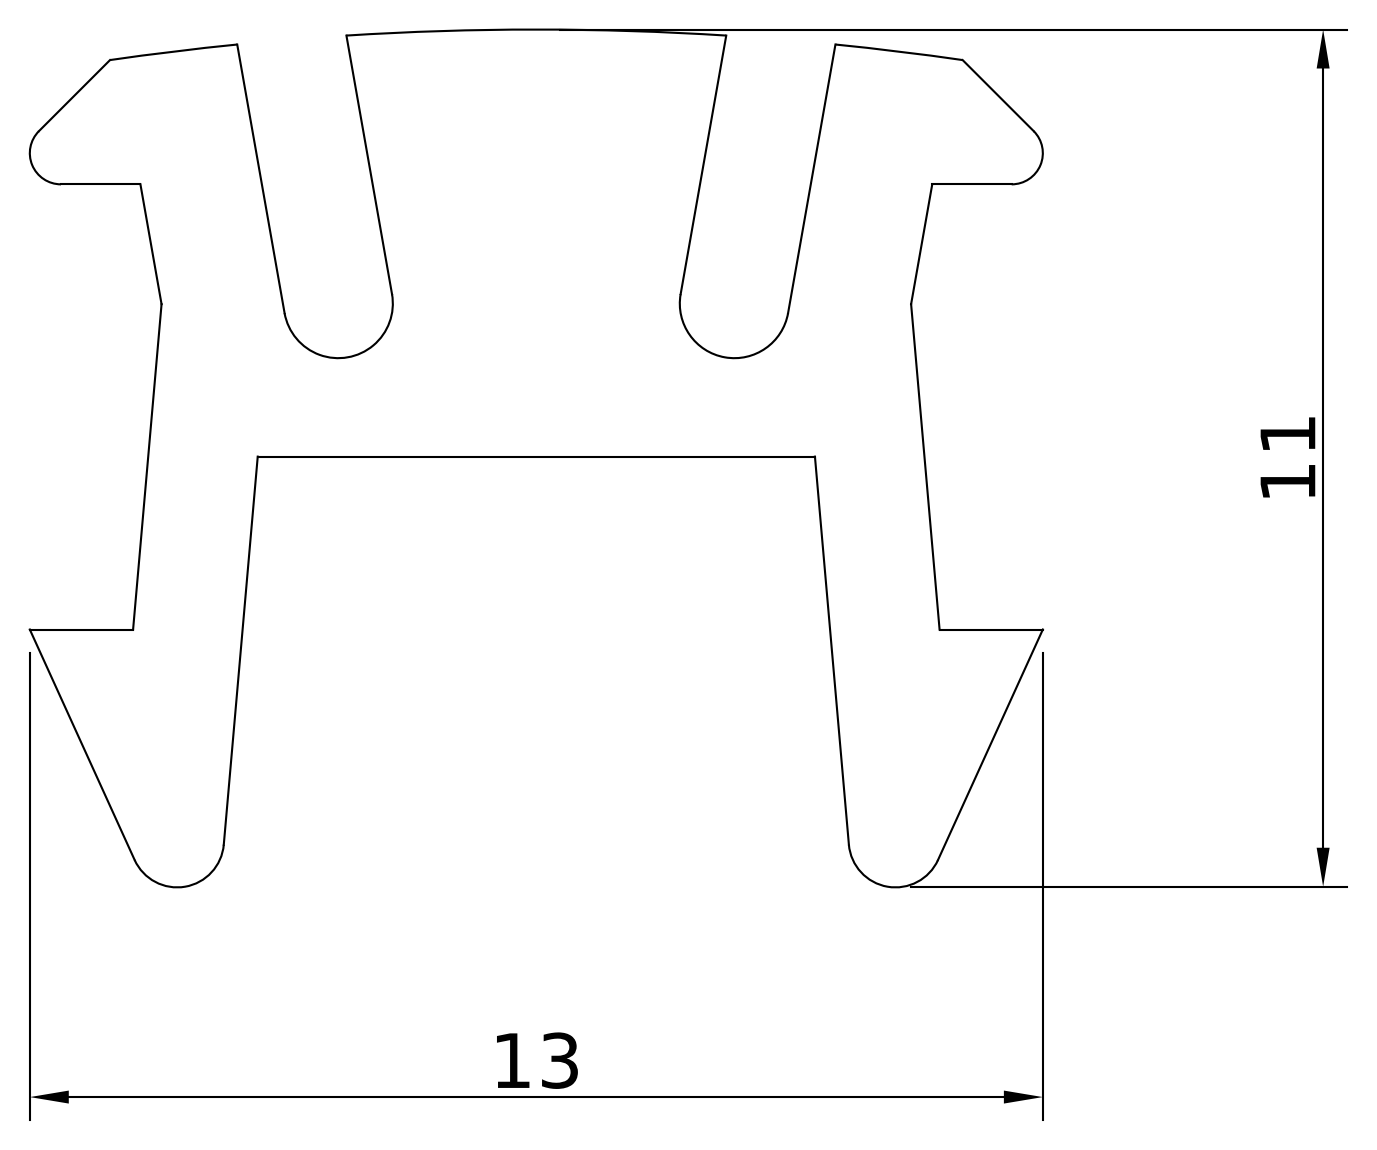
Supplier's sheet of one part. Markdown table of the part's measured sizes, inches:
| quantity | value |
| --- | --- |
| part name | CGUCA0000001 |
| STEP written by | Autodesk Inventor 2019 (AUTOMOTIVE_DESIGN) |
| units | inches |
| bodies | 1 solid, 30 faces (21 planar, 9 cylindrical, 0 other) |
| overall size | 3.937 × 0.512 × 0.433 |
| volume | 0.39 in³ |
| surface area | 11.63 in² |
| partial cylindrical surfaces (radius × count) | 0.016 × 2, 0.024 × 2, 0.028 × 2, 1.512 × 1 |
| main face-to-face distances | 0.055, 0.061, 0.116, 0.087, 0.225, 0.137, 3.937 |
